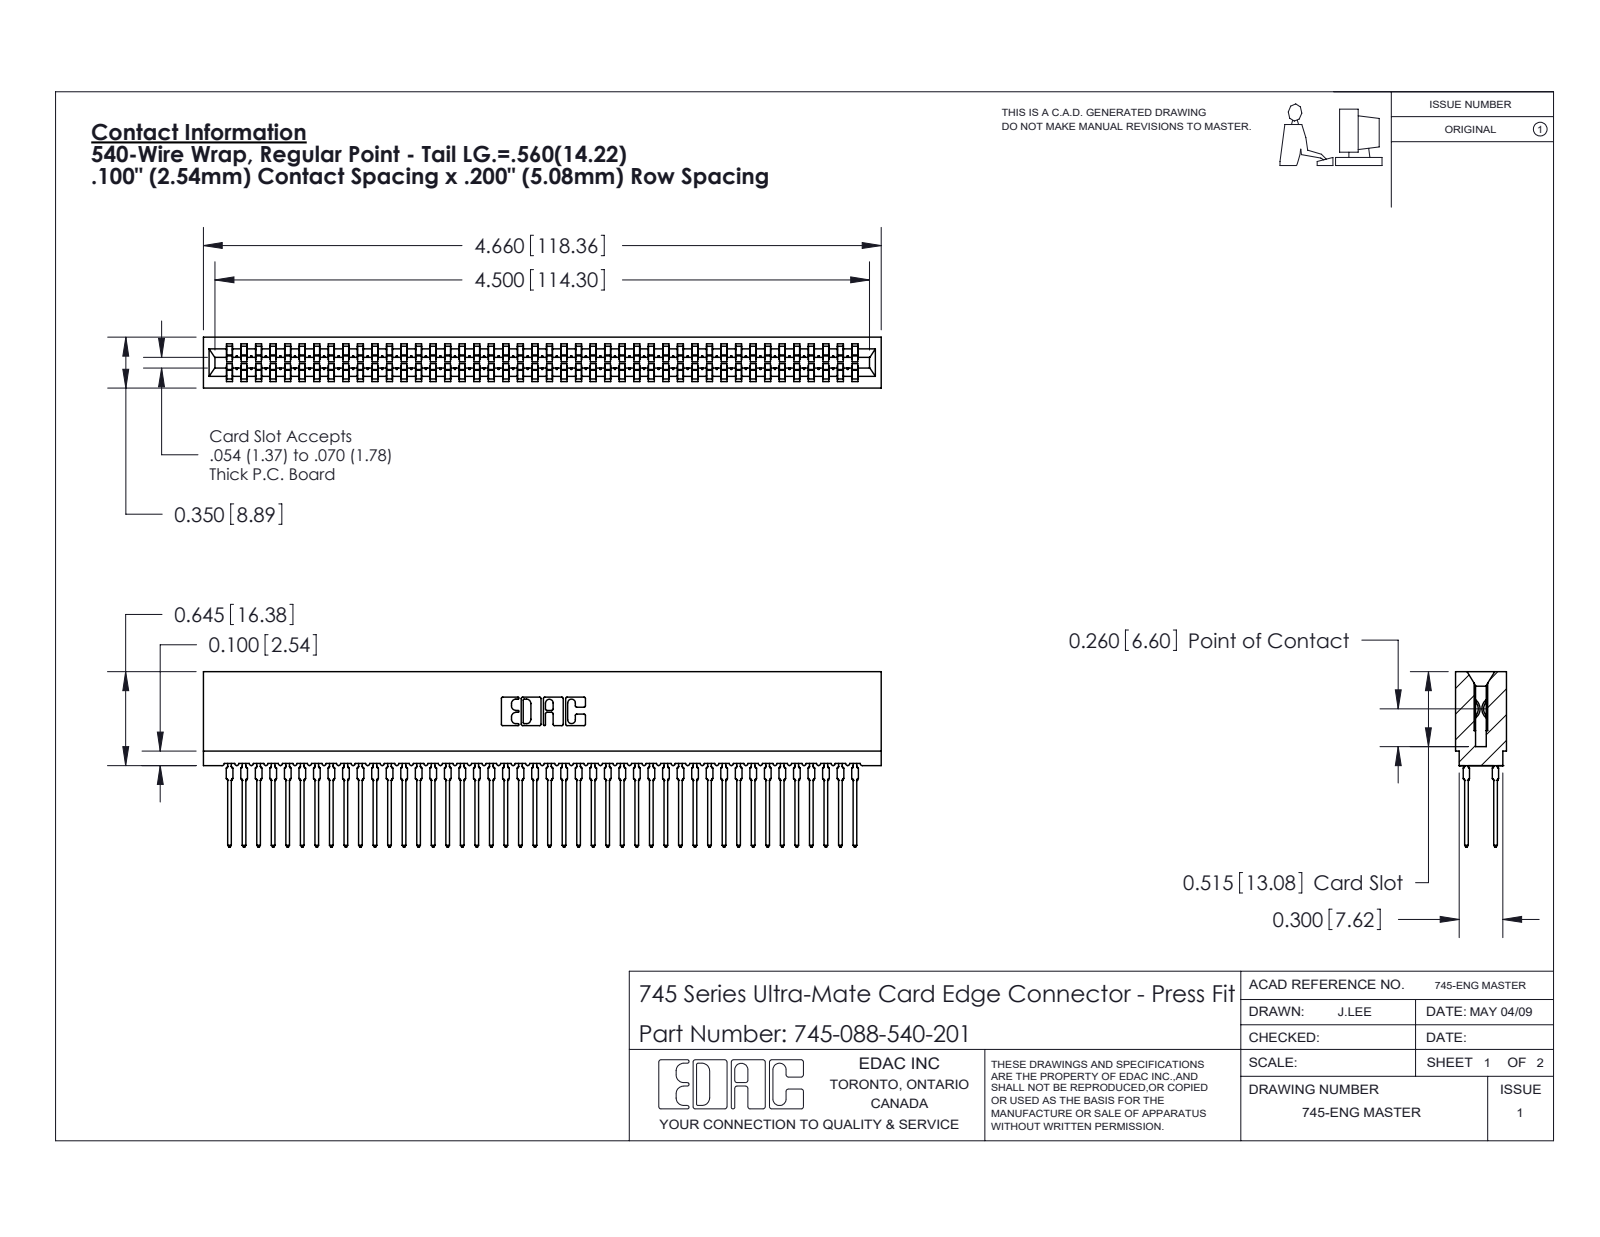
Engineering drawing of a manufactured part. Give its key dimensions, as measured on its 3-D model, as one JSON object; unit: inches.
{"part_name": "745 Part_Insulator Option - 01; 745-088-540-201; 745-292-001_540", "step_written_by": "SolidWorks 2020 (CONFIG_CONTROL_DESIGN)", "units": "inches", "bodies": {"solids": 89, "faces": 7971, "planar": 4103, "cylindrical": 1580, "other": 2288}, "overall_size": [4.66, 1.206, 0.35], "volume_in3": 0.666, "surface_area_in2": 36.02, "partial_cylinders_radius": [[0.021, 176], [0.015, 88], [0.01, 22], [0.005, 8], [0.011, 8], [0.007, 6], [0.031, 6], [0.026, 3]], "face_to_face_distances": [0.063, 0.287, 0.35, 0.2, 0.045, 0.305, 0.018, 0.243, 0.138, 0.212]}
